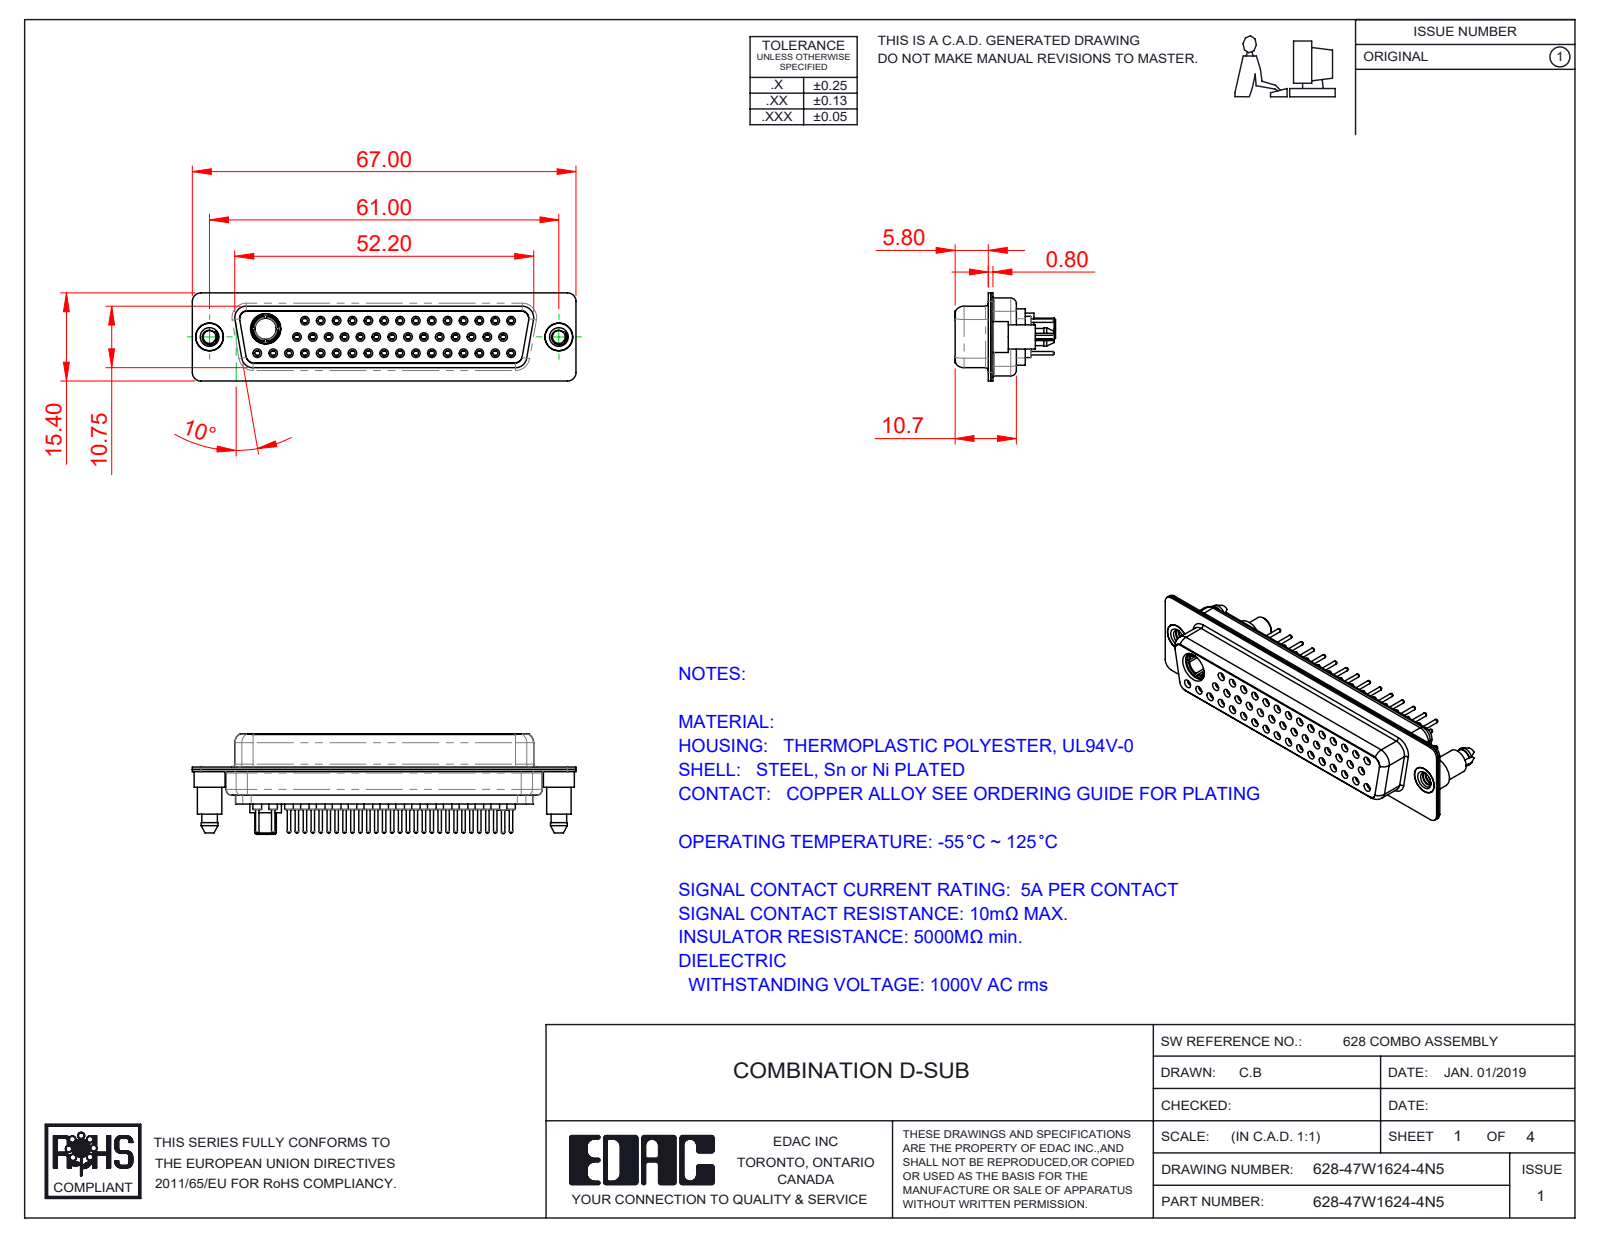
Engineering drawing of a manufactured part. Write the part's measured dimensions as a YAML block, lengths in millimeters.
part_name: "628Combo Housing_47W1; 628Combo Contact Row 3_24; 628Combo Threaded Boardlock_5; 628Combo Shell Front_50 Contacts (+5 more)"
step_written_by: "SolidWorks 2016 (CONFIG_CONTROL_DESIGN)"
units: millimeters
bodies: {solids: 53, faces: 2921, planar: 799, cylindrical: 1058, other: 1064}
overall_size: [67, 17.55, 15.4]
volume: 7238
surface_area: 15034
round_holes:
  - {diameter: 1.1, count: 46}
  - {diameter: 0.9, count: 45}
  - {diameter: 1.5, count: 45}
  - {diameter: 2, count: 45}
  - {diameter: 1.6, count: 31}
  - {diameter: 1.7, count: 14}
  - {diameter: 4.85, count: 3}
  - {diameter: 2.26, count: 2}
  - {diameter: 4, count: 2}
  - {diameter: 4.05, count: 2}
  - {diameter: 3.7, count: 1}
  - {diameter: 5.3, count: 1}
round_bosses_or_shafts:
  - {diameter: 2.2, count: 46}
  - {diameter: 0.6, count: 46}
  - {diameter: 1.6, count: 15}
  - {diameter: 5.4, count: 2}
  - {diameter: 4.95, count: 2}
  - {diameter: 4.8, count: 2}
  - {diameter: 4.25, count: 2}
  - {diameter: 5.5, count: 1}
partial_cylinders:
  - {radius: 1.5, count: 18}
  - {radius: 1.35, count: 12}
  - {radius: 2, count: 12}
  - {radius: 1.6, count: 10}
  - {radius: 0.25, count: 4}
  - {radius: 0.5, count: 4}
  - {radius: 0.6, count: 4}
  - {radius: 0.65, count: 4}
face_to_face_distances: [0.4, 11.33, 6.45, 6.05, 1.87, 12.25, 6.2, 5.8, 10.35, 10.93]
hole_center_spacings: [3.16, 2.77, 5.54, 8.31, 11.08, 13.85, 16.62, 19.39]
